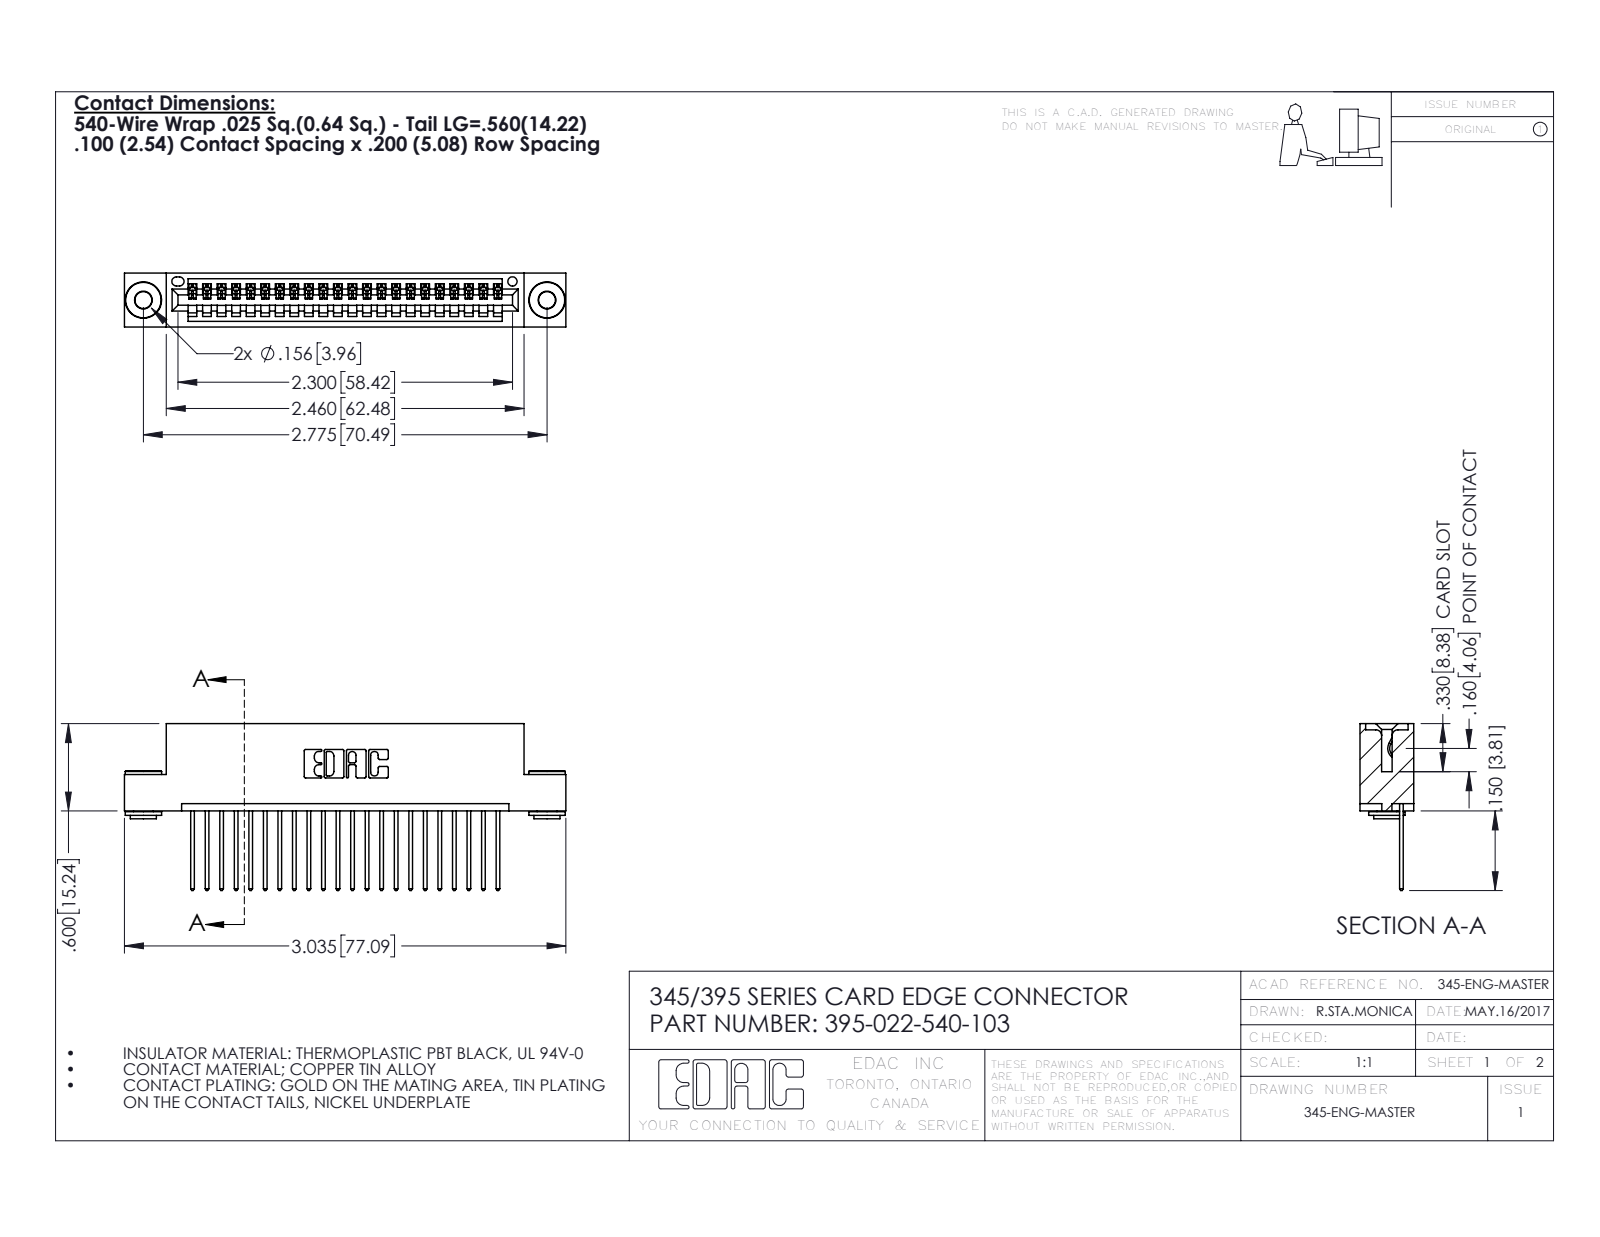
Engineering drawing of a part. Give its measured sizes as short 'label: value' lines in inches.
name: 345 Part_Flush Mounting Lugs - 0.156 Dia-TH; 345-250-002_345-250-002-102; 345-292-001_345-293-140; 395-022-540-103
written by: SolidWorks 2016 (CONFIG_CONTROL_DESIGN)
unit: in
bodies: 25 solids, 1440 faces (970 planar, 462 cylindrical, 8 other)
size: 3.035 × 1.147 × 0.37
volume: 0.44 in³; area: 15.09 in²
holes: 2× ⌀0.116, 2× ⌀0.156, 1× ⌀0.064
bosses: 2× ⌀0.25, 2× ⌀0.18, 2× ⌀0.136
rounds: 44× R0.006, 44× R0.01, 22× R0.01, 6× R0.007, 6× R0.031, 3× R0.026, 2× R0.031, 2× R0.04
face distances: 0.072, 0.298, 0.2, 0.37, 0.025, 0.098, 0.272, 0.225, 0.149, 0.072
hole spacings: 0.27, 2.541, 2.775
